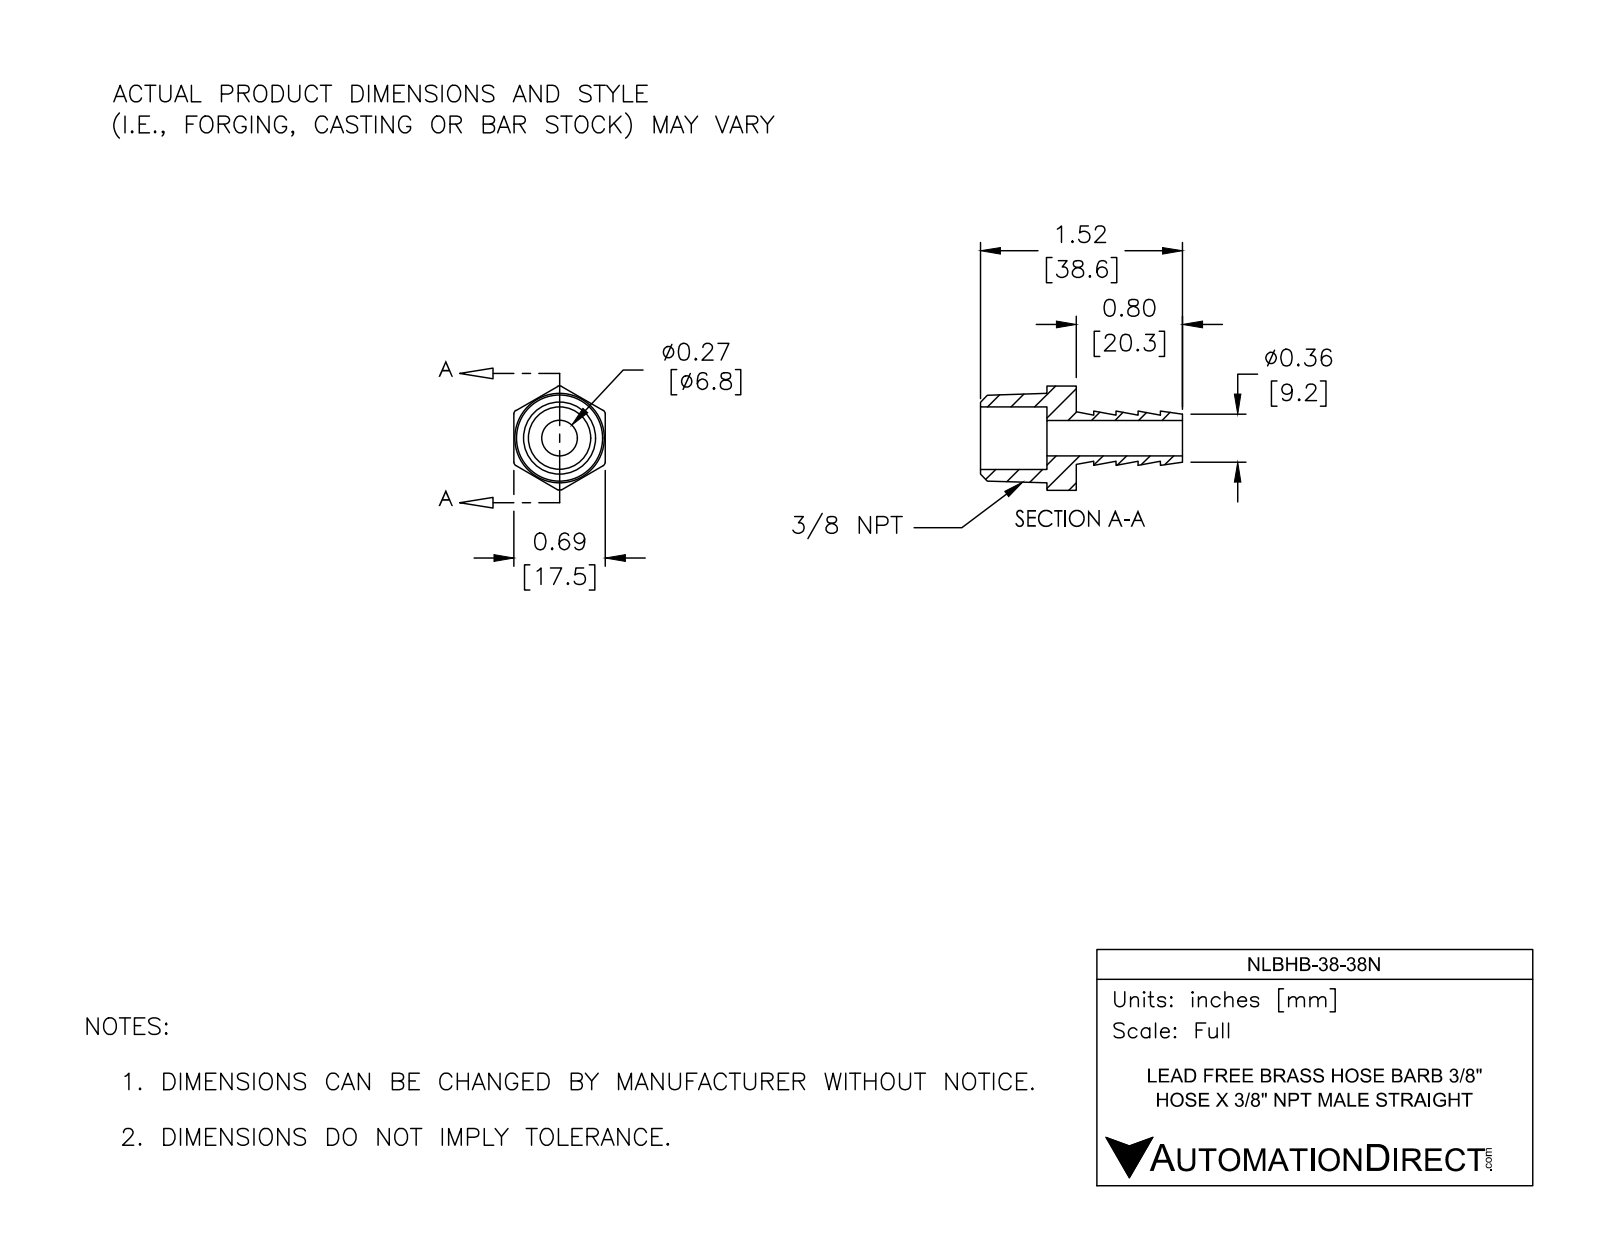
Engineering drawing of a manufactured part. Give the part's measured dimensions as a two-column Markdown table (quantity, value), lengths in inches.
| quantity | value |
| --- | --- |
| part name | NLBHB-38-38N |
| STEP written by | SolidWorks 2017 (AUTOMOTIVE_DESIGN) |
| units | inches |
| bodies | 1 solid, 39 faces (15 planar, 10 cylindrical, 14 other) |
| overall size | 1.52 × 0.785 × 0.687 |
| volume | 0.203 in³ |
| surface area | 4.841 in² |
| round holes (diameter × count) | 0.267 × 1, 0.47 × 1 |
| partial cylindrical surfaces (radius × count) | 0.03 × 6 |
| main face-to-face distances | 0.687, 0.22, 0.167, 0.334, 0.501, 0.72, 0.5, 0.8, 1.02, 1.52 |
